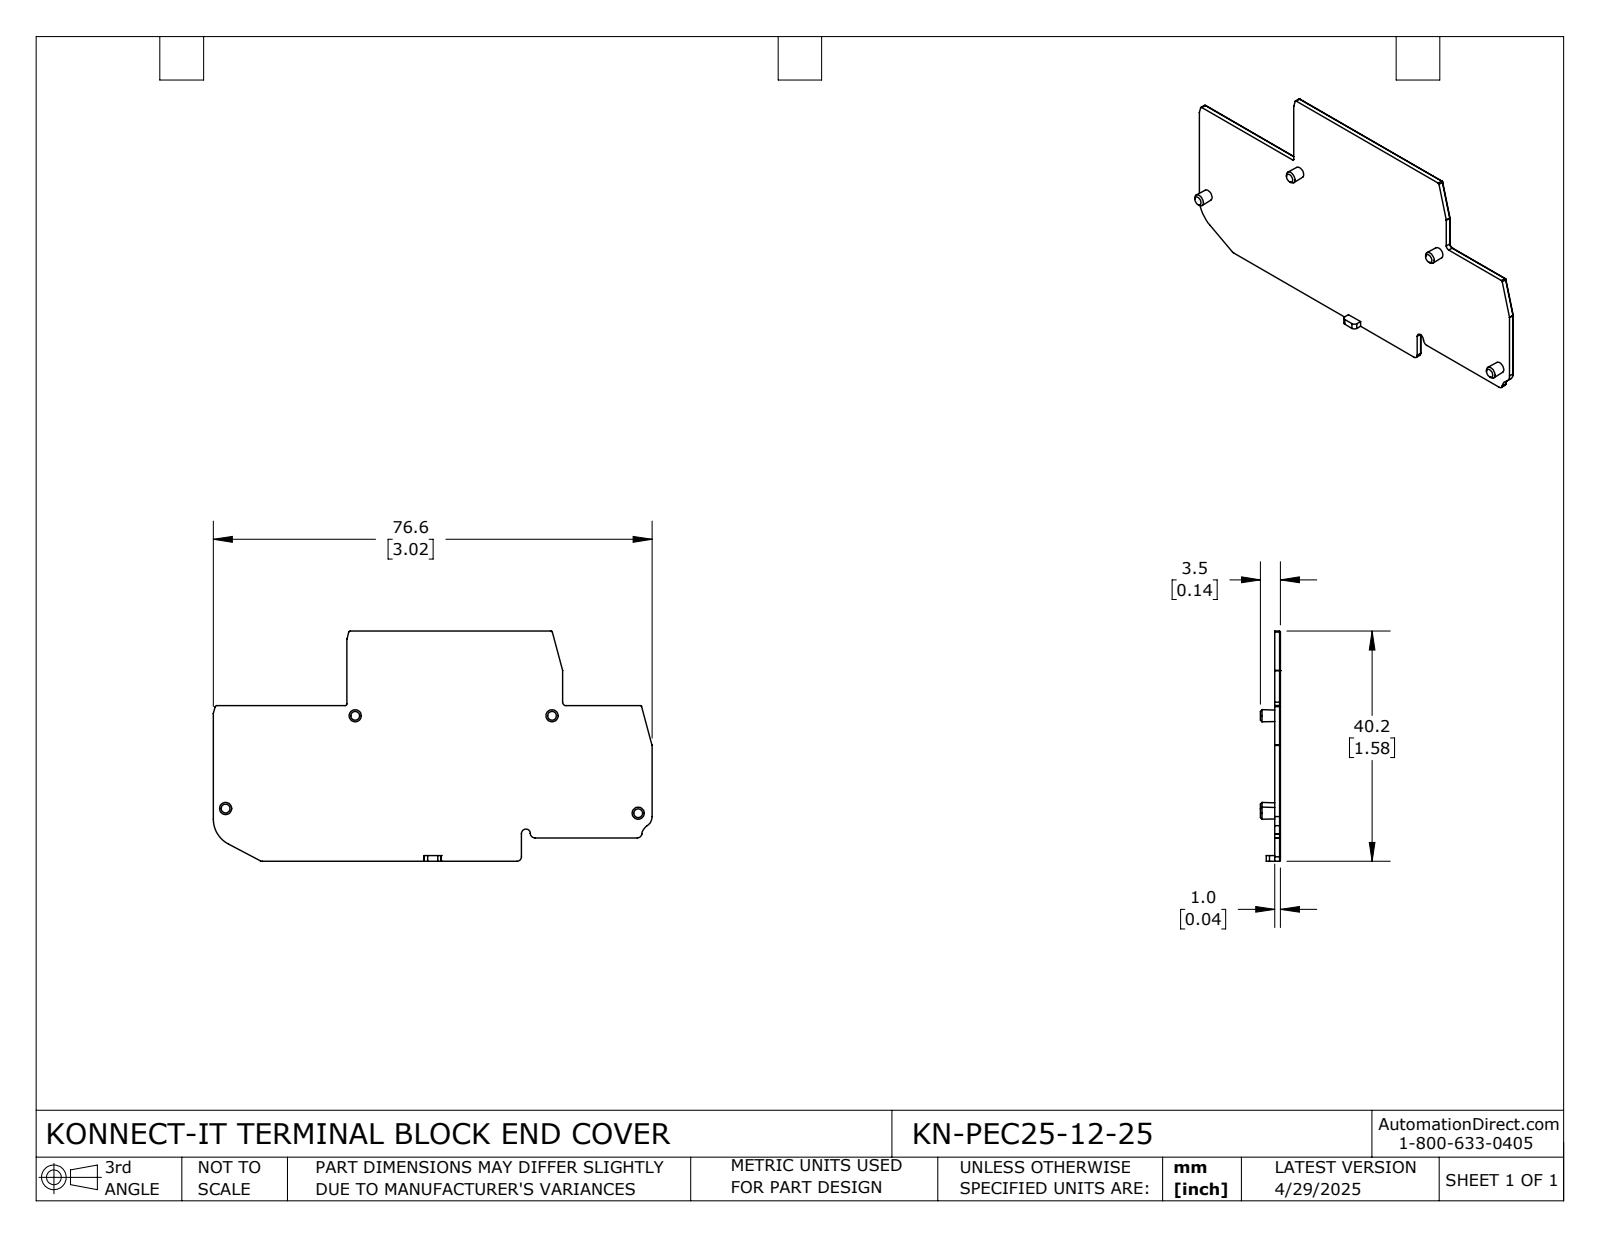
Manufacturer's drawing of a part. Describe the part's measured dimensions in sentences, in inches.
The part is named "KN-PEC25-12-25". Its 3-D file was written by "SolidWorks 2024 (CONFIG_CONTROL_DESIGN)". It is 1 solid with 99 faces: 45 planar, 38 cylindrical and 16 other. Overall it measures 3.016 by 1.582 by 0.138 inches. Its volume is 0.151 cubic inches and its surface area 8.024 square inches. Partial cylindrical surfaces (rounded edges, fillets, slot ends): 8 of radius 0.008, 6 of radius 0.012, 5 of radius 0.028, 4 of radius 0.031, 3 of radius 0.004, 3 of radius 0.024, 1 of radius 0.016, 1 of radius 0.031. The main face-to-face distances are 0.039, 0.512, 1.07, 1.582, 0.033, 0.161, 0.909, 1.422, 1.066, 1.578.
